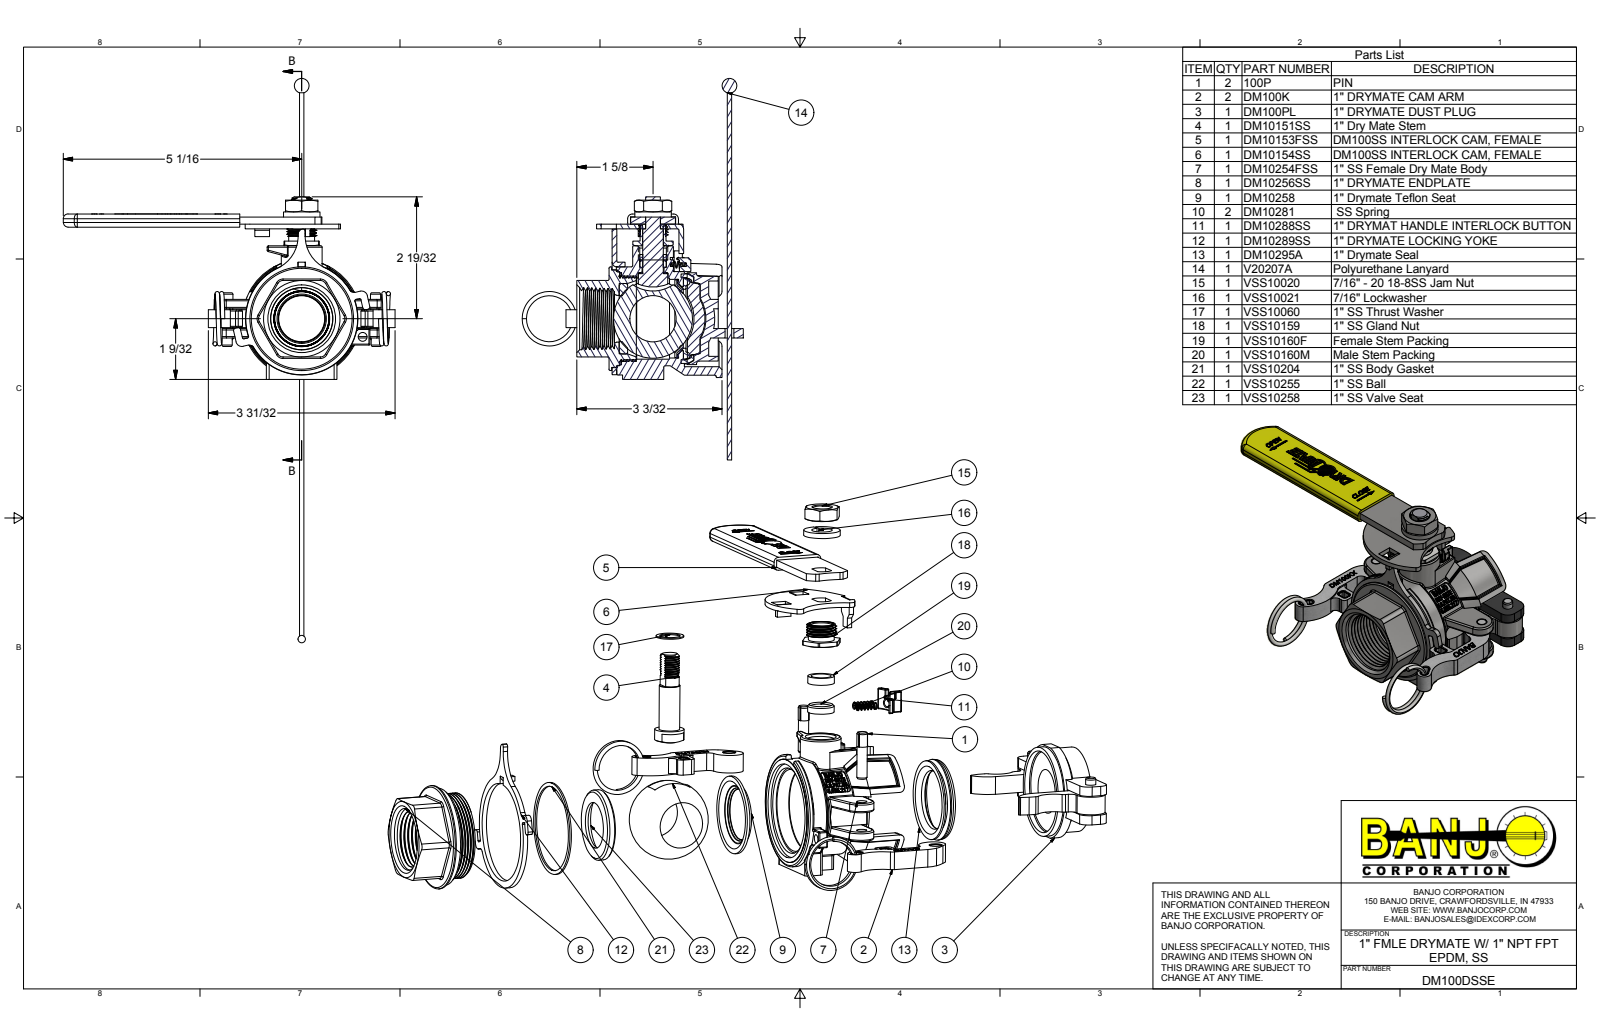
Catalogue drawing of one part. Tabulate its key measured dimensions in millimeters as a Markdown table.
| quantity | value |
| --- | --- |
| part name | 100P; DM10151SS; DM10281; V20207A (+8 more) |
| STEP written by | Autodesk Inventor 2016 (AUTOMOTIVE_DESIGN) |
| units | millimeters |
| bodies | 38 solids, 2859 faces (1312 planar, 592 cylindrical, 955 other) |
| overall size | 304.4 × 179.01 × 125.36 |
| volume | 200 800 mm³ |
| surface area | 130 155 mm² |
| round holes (diameter × count) | 3.17 × 3, 5.54 × 2, 5.56 × 2, 5.71 × 2, 5.79 × 2, 6.22 × 2, 4.76 × 1, 4.78 × 1, 9.73 × 1, 10.97 × 1, 11.02 × 1, 11.13 × 1 |
| round bosses / shafts (diameter × count) | 5.77 × 4, 5.51 × 4, 5.59 × 3, 0.25 × 2, 60.71 × 1, 55.88 × 1, 52.58 × 1, 50.8 × 1 |
| partial cylindrical surfaces (radius × count) | 0.76 × 69, 0.4 × 50, 0.51 × 27, 2.54 × 21, 3.17 × 14, 1.02 × 8, 1.52 × 8, 2.29 × 8 |
| main face-to-face distances | 1.65, 3.94, 5.46, 1.52, 3.81, 5.59, 15.24, 5.58, 5.08, 0.5 |
| hole center spacings | 15.77, 27.32, 20.22, 40.88, 42.21, 48.32, 52.79, 82.62 |
